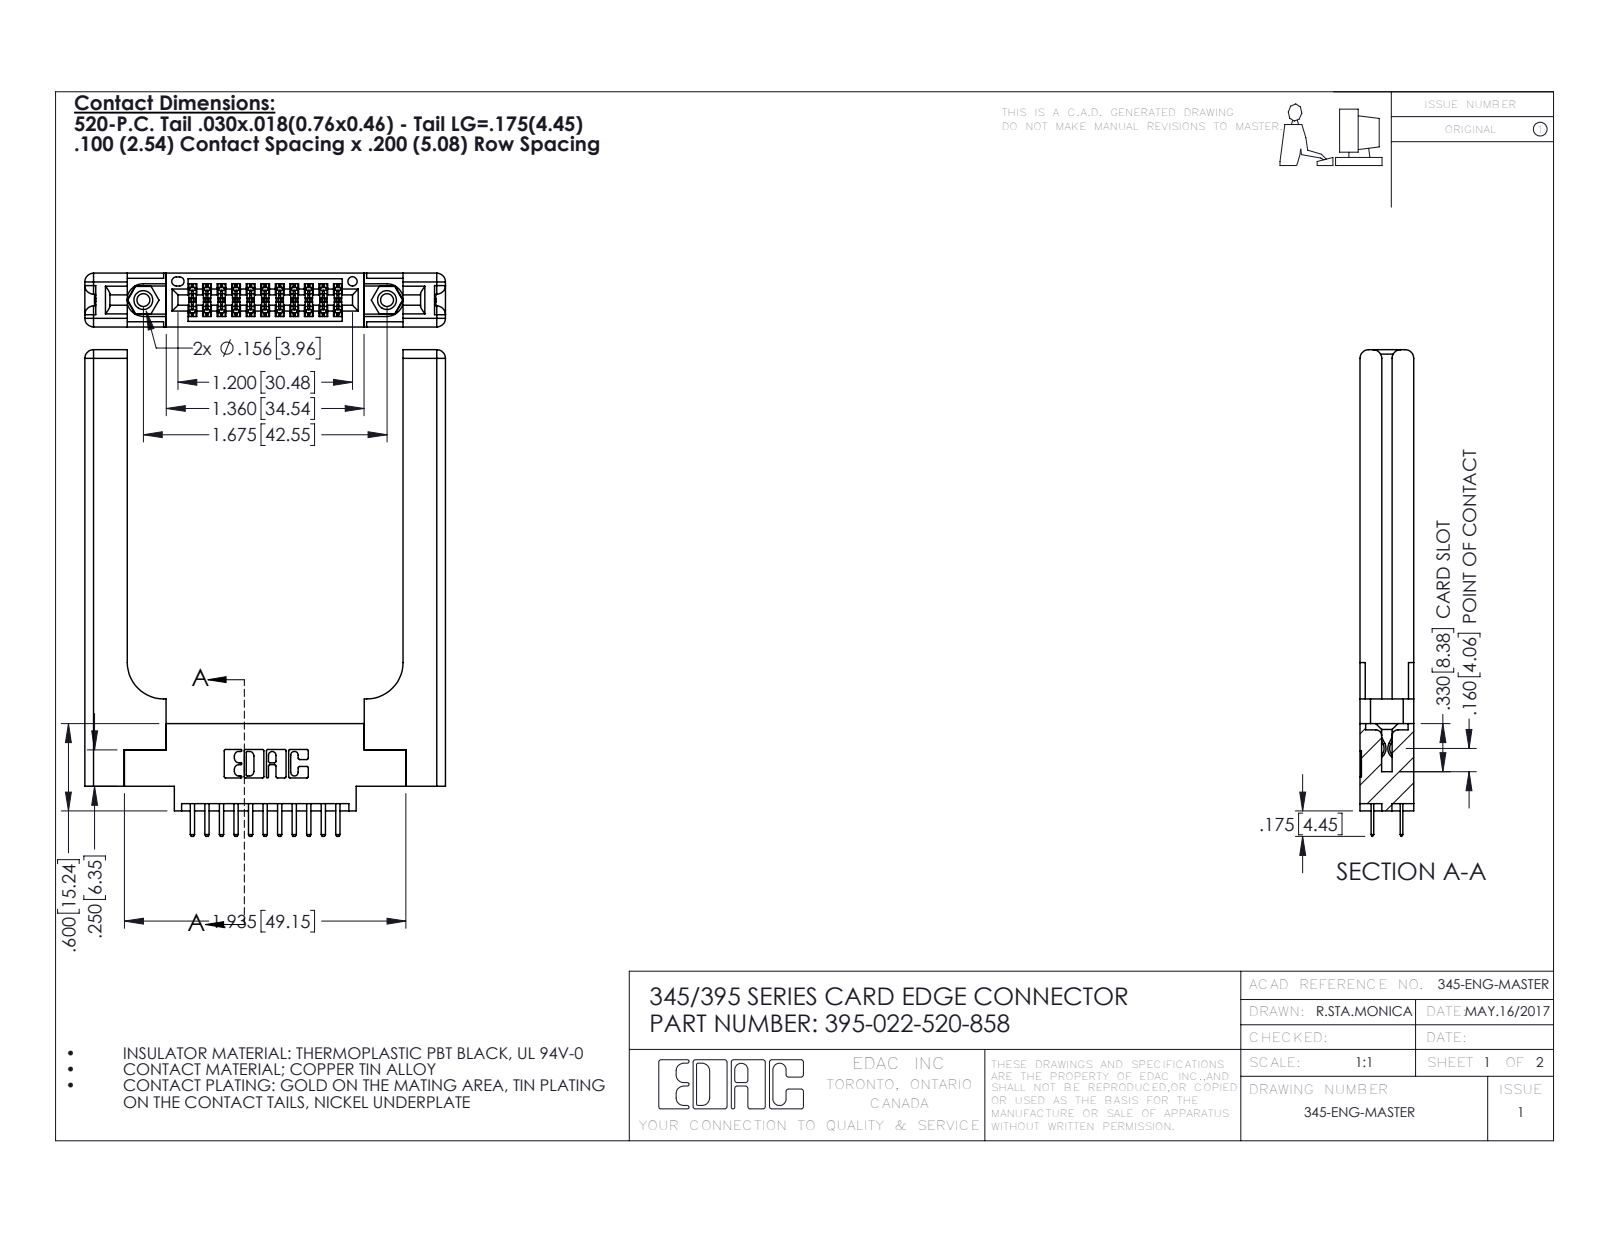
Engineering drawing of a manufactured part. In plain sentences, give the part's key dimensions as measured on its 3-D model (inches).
The part is named "345-250-001_345-250-001-102; 345 Part_0.170 Offset - 0.156 Dia-TH; 345-292-001_345-293-120; 395-022-520-858 (+1 more)". Its 3-D file was written by "SolidWorks 2016 (CONFIG_CONTROL_DESIGN)". It is 27 solids with 1574 faces: 1002 planar, 512 cylindrical and 60 other. Overall it measures 3.345 by 2.479 by 0.37 inches. Its volume is 0.865 cubic inches and its surface area 20.17 square inches. Round holes: 2 of diameter 0.089, 2 of diameter 0.125, 2 of diameter 0.156, 1 of diameter 0.064. Round bosses or shafts: 2 of diameter 0.155. Partial cylindrical surfaces (rounded edges, fillets, slot ends): 33 of radius 0.006, 26 of radius 0.01, 22 of radius 0.01, 16 of radius 0.06, 6 of radius 0.007, 6 of radius 0.031, 3 of radius 0.026, 2 of radius 0.014. The main face-to-face distances are 0.37, 0.072, 0.15, 0.22, 0.298, 0.077, 0.148, 1.896, 0.2, 0.225. The hole center spacings are 0.27, 1.443, 1.675.
